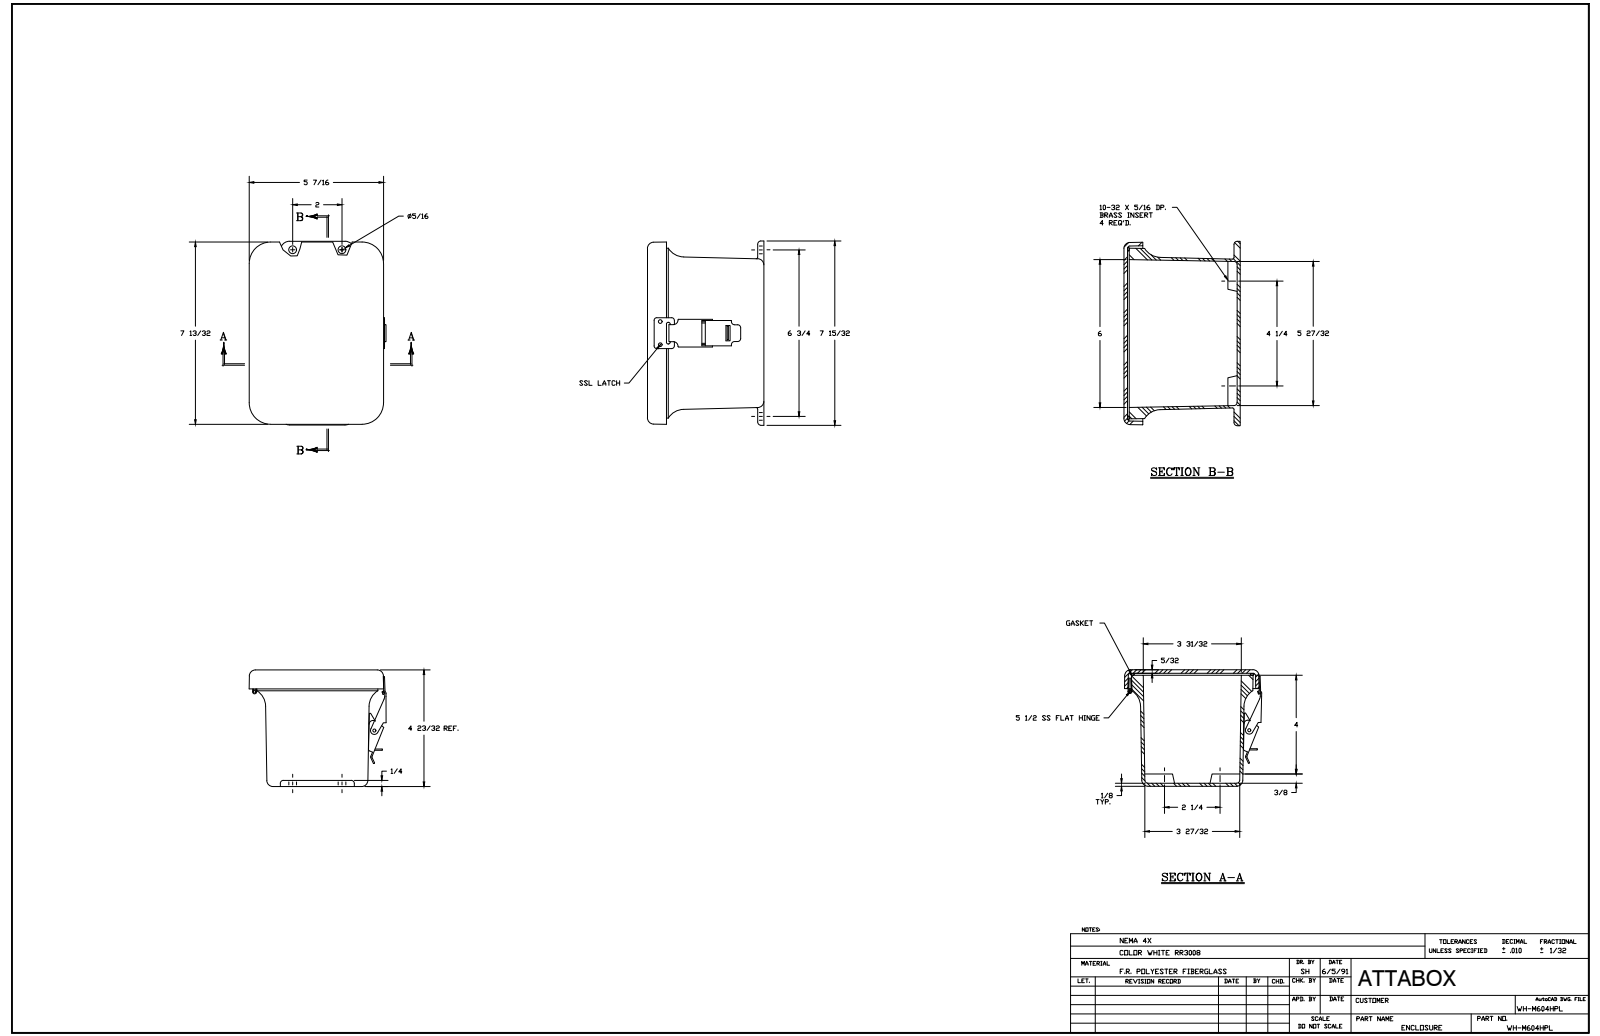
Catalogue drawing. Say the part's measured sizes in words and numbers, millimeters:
The part is named "WH-M604HPL". Its 3-D file was written by "SolidWorks 2018 (AUTOMOTIVE_DESIGN)". It is 25 solids with 627 faces: 249 planar, 254 cylindrical and 124 other. Overall it measures 189.8 by 142.8 by 119.8 millimeters. Its volume is 518 000 cubic millimeters and its surface area 263 100 square millimeters. Round holes: 11 of diameter 3.6, 5 of diameter 3.3, 5 of diameter 3.9, 4 of diameter 2.6, 4 of diameter 4, 4 of diameter 5.5, 2 of diameter 3.3, 2 of diameter 3.4, 1 of diameter 2.2, 1 of diameter 3.4, 1 of diameter 9.5. Round bosses or shafts: 6 of diameter 3.2, 5 of diameter 6.4, 4 of diameter 6.9, 3 of diameter 3.2, 1 of diameter 7.6, 1 of diameter 4.3, 1 of diameter 3.9, 1 of diameter 3. Partial cylindrical surfaces (rounded edges, fillets, slot ends): 20 of radius 0.8, 16 of radius 3.2, 12 of radius 0.4, 8 of radius 1.1, 8 of radius 6.4, 6 of radius 0.8, 4 of radius 0.6, 4 of radius 1.5. The main face-to-face distances are 3.7, 116.2, 119.8, 3.2, 113, 116.7, 114.3, 111.1, 1.9, 5.5. The hole center spacings are 23.8, 63.5, 84.8, 19.1, 11.9, 12.7, 34.1, 37.3.
